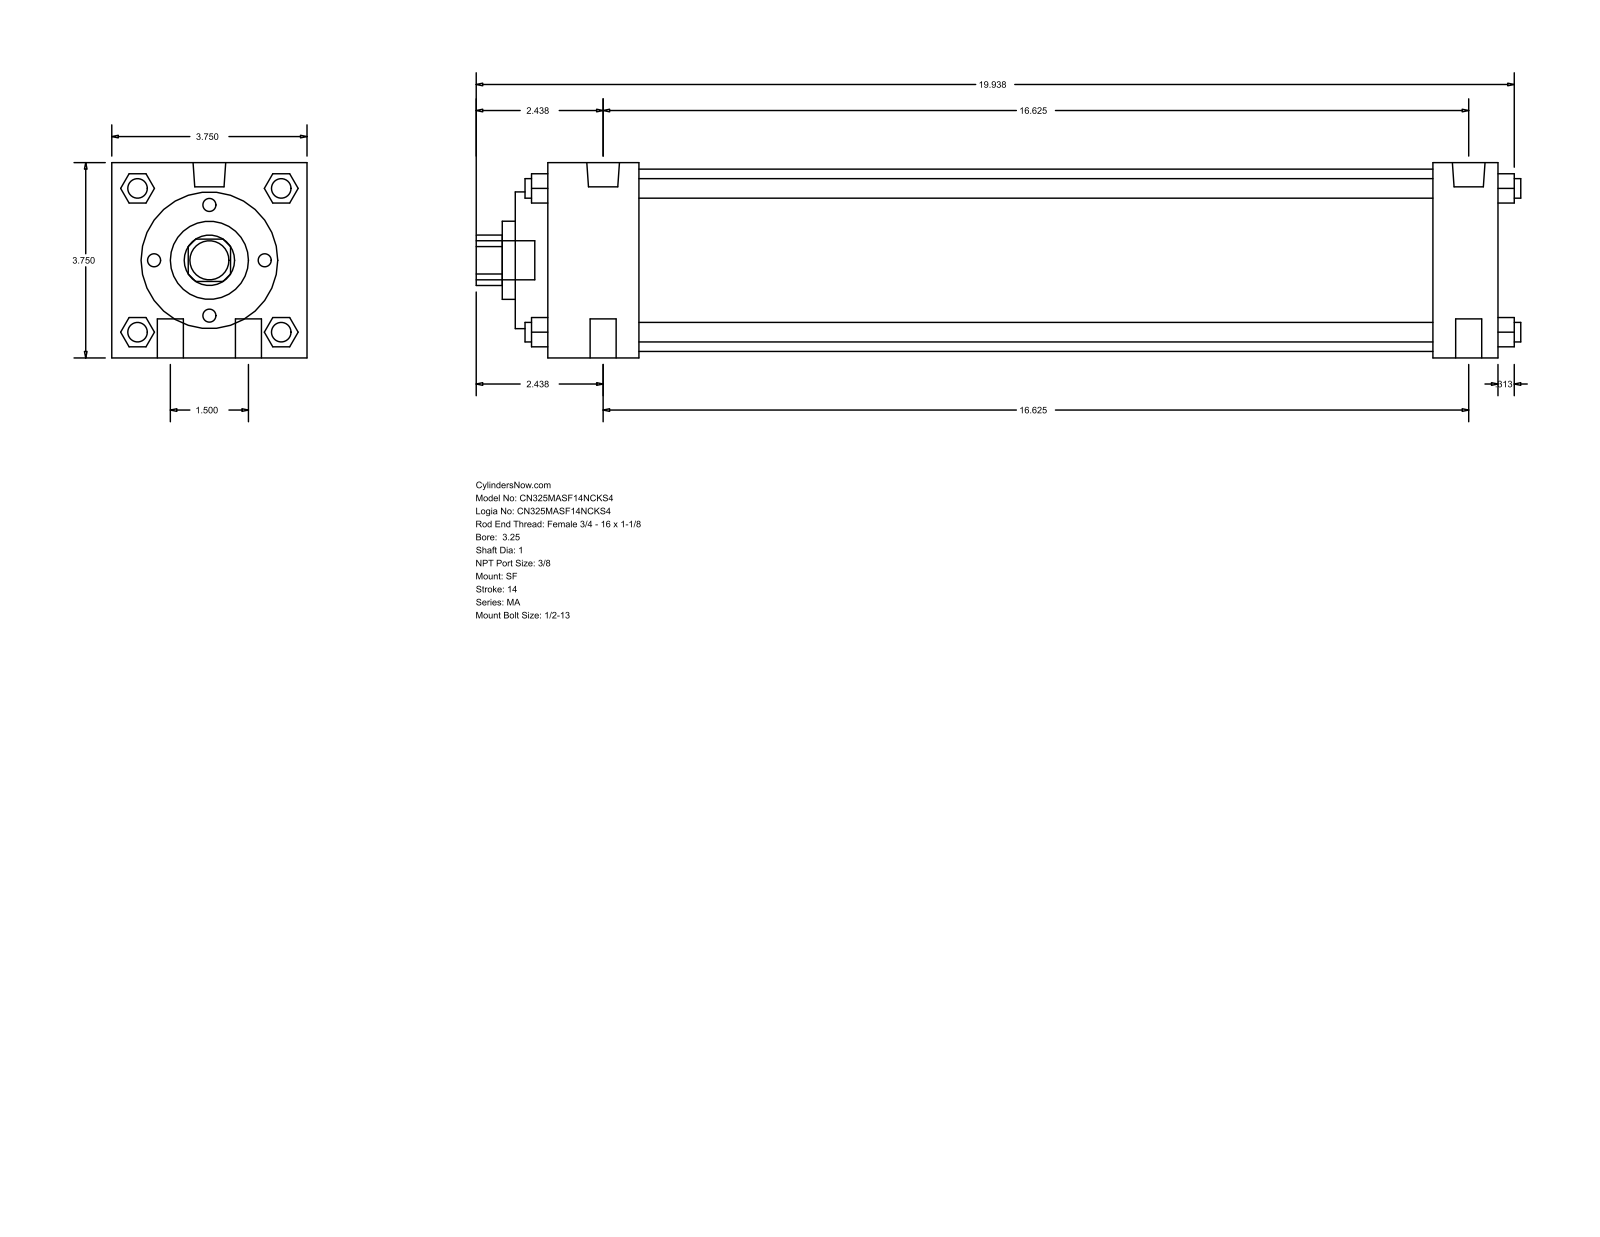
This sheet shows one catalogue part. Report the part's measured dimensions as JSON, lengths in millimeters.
{"part_name": "MA_SF__0325_1", "step_written_by": "GSSL Pune (CONFIG_CONTROL_DESIGN)", "units": "millimeters", "bodies": {"solids": 0, "faces": 126, "planar": 95, "cylindrical": 31, "other": 0}, "overall_size": [509.59, 95.25, 95.25], "round_holes": [[25.4, 1], [38.1, 1], [66.67, 1], [88.9, 1]], "round_bosses_or_shafts": [[12.7, 4], [9.53, 4], [15.93, 2], [11.11, 2], [19.05, 1]], "partial_cylinders_radius": [[12.29, 1]], "face_to_face_distances": [95.24, 463.56, 15.87, 431.81, 31.75, 44.46, 387.35, 419.1, 60.33, 447.68]}
